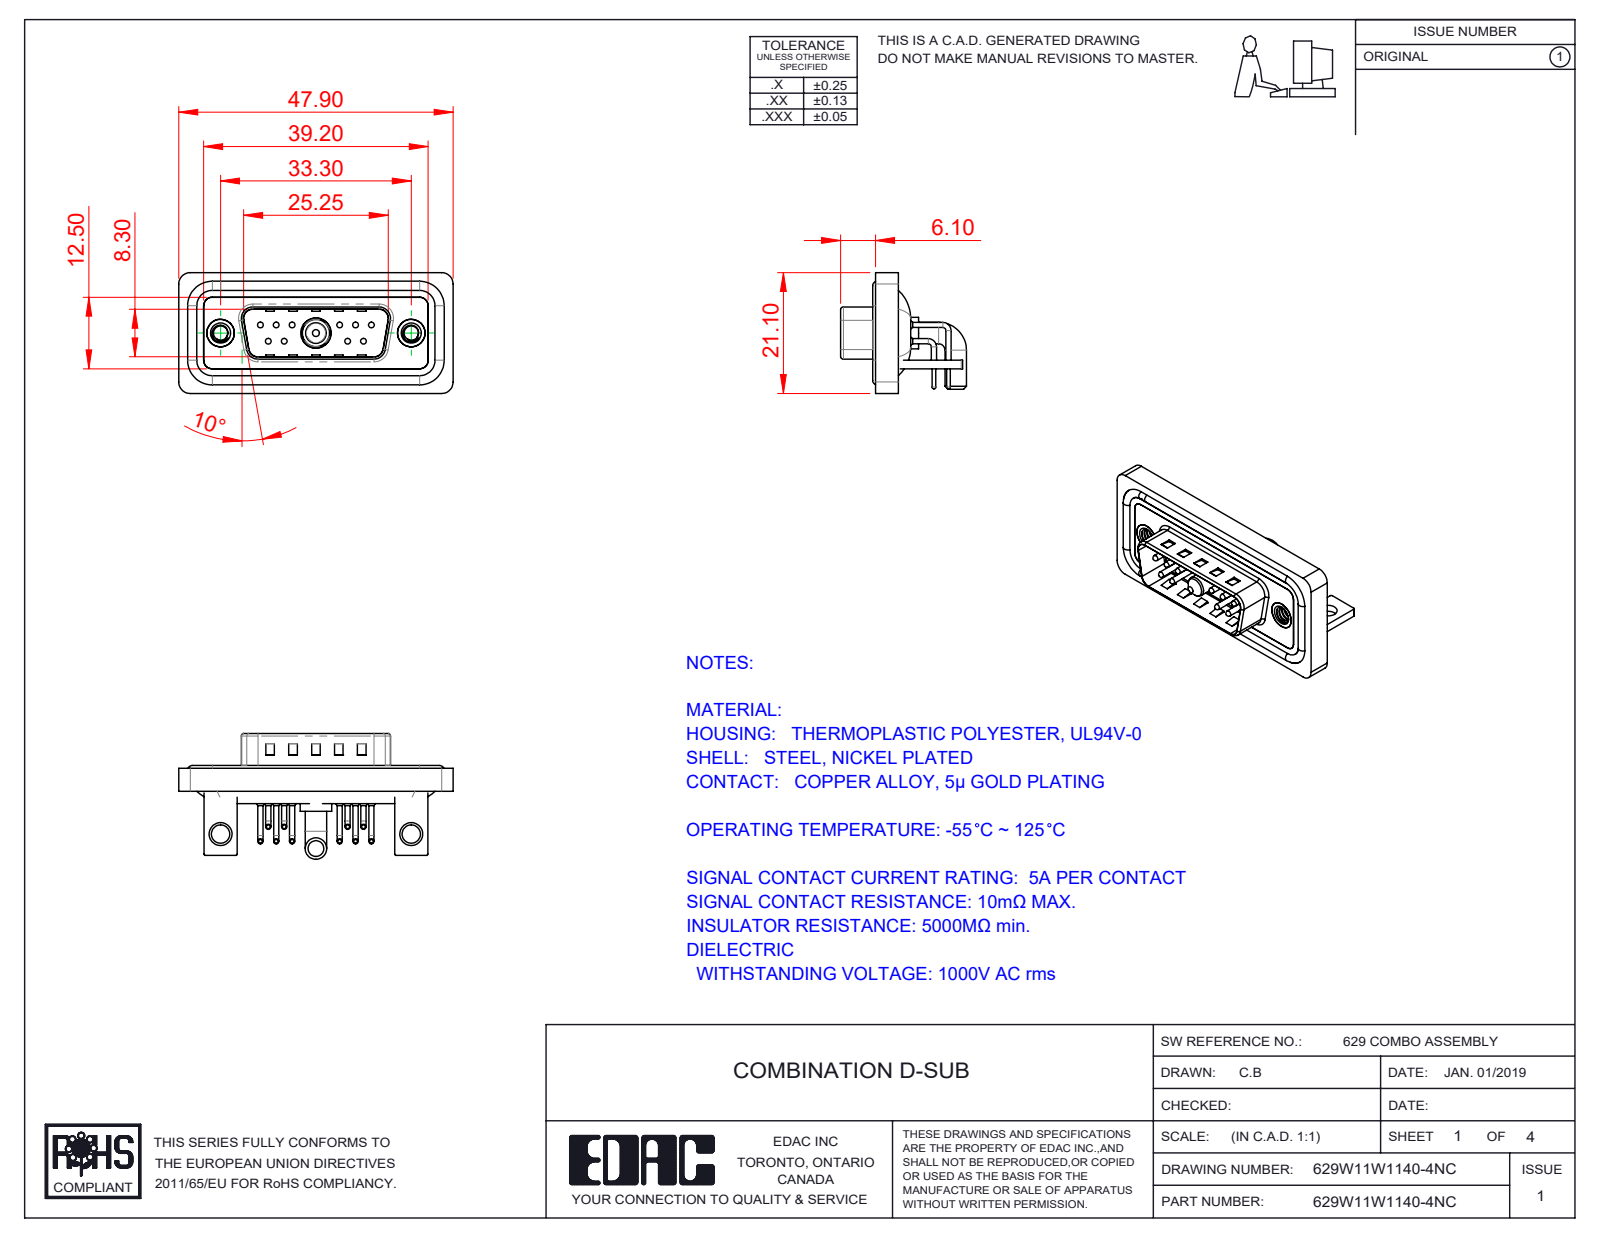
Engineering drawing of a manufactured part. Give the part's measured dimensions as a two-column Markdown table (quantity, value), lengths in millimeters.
| quantity | value |
| --- | --- |
| part name | 629Combo Shell Rear_15 Contacts; 629W11W1140-4NC; 629Combo Threaded Rivet_B; 629Combo Waterproof Housing_15 Contacts (+6 more) |
| STEP written by | SolidWorks 2020 (CONFIG_CONTROL_DESIGN) |
| units | millimeters |
| bodies | 21 solids, 1641 faces (856 planar, 587 cylindrical, 198 other) |
| overall size | 47.9 × 21.98 × 21.1 |
| volume | 5 934 mm³ |
| surface area | 9 912 mm² |
| round holes (diameter × count) | 0.75 × 10, 1.6 × 10, 2 × 10, 2.5 × 2, 3.2 × 2, 4 × 2, 4.8 × 2, 5 × 2, 4.85 × 1, 5.3 × 1 |
| round bosses / shafts (diameter × count) | 0.9 × 20, 1.5 × 10, 1 × 10, 0.65 × 10, 1.6 × 4, 4.9 × 2, 3.75 × 2, 5.5 × 1 |
| partial cylindrical surfaces (radius × count) | 2 × 21, 1.5 × 18, 0.25 × 16, 1.01 × 10, 0.5 × 9, 1.6 × 8, 1 × 7, 0.6 × 4 |
| main face-to-face distances | 0.4, 0.8, 1.5, 2.9, 2.1, 1.1, 1.6, 1.2, 3.7, 4.1 |
| hole center spacings | 3.16, 2.77, 13.85, 11.08, 16.62, 5.03, 5.04, 5.54 |
